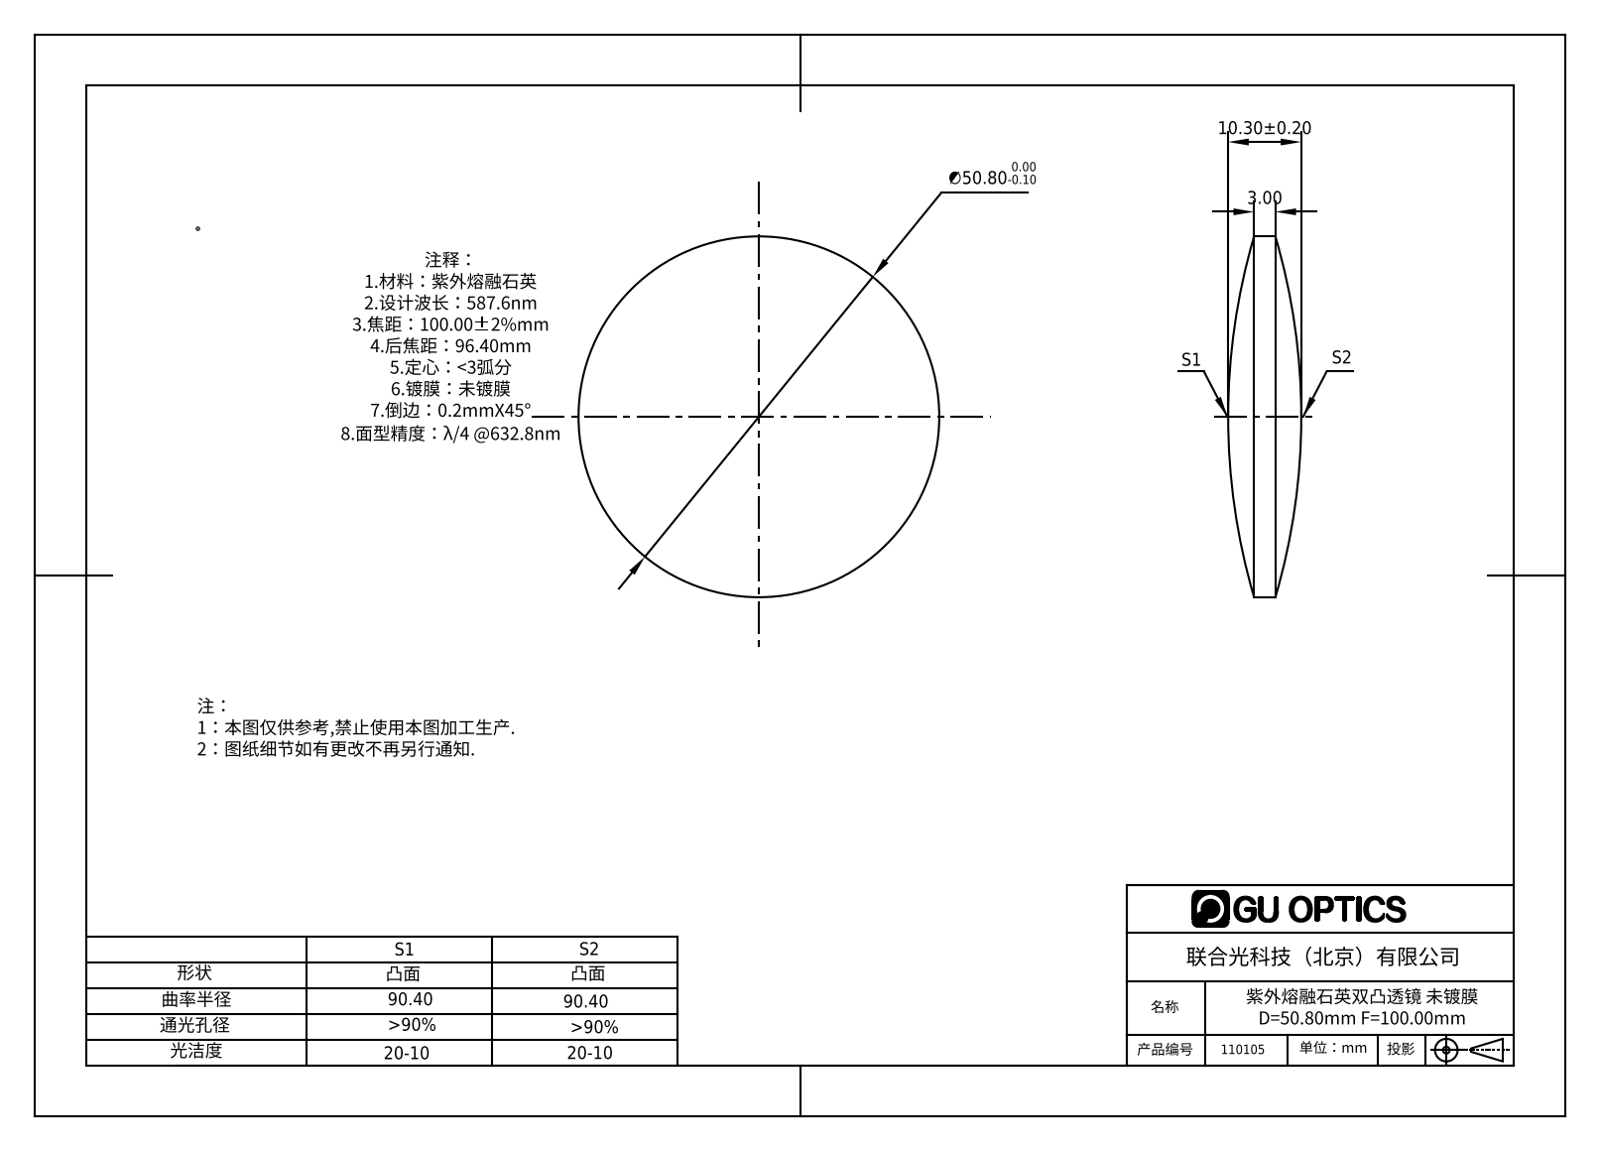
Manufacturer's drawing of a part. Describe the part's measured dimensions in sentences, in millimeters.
The part is named "110105". Its 3-D file was written by "SolidWorks 2016 (CONFIG_CONTROL_DESIGN)". It is 1 solid with 6 faces: 0 planar, 2 cylindrical and 4 other. Overall it measures 50.8 by 50.8 by 10.3 millimeters. Its volume is 13 529 cubic millimeters and its surface area 4 616 square millimeters. Round bosses or shafts: 1 of diameter 50.8.
